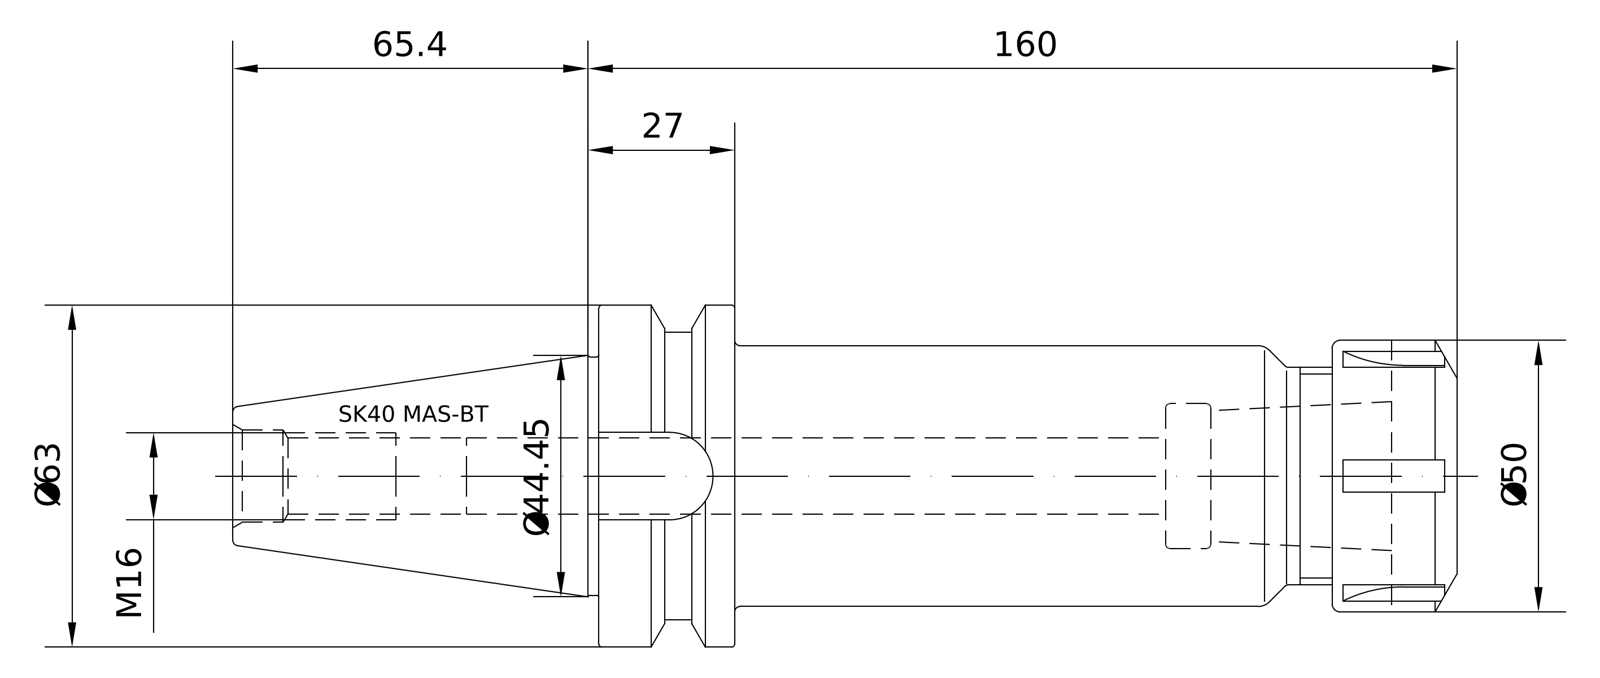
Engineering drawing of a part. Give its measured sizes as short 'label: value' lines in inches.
name: 40-522-32; 83-912-32; 40-522-32_ASM
written by: PRO/ENGINEER BY PARAMETRIC TECHNOLOGY CORPORATION, 2010430 (CONFIG_CONTROL_DESIGN)
unit: in
bodies: 2 solids, 146 faces (52 planar, 32 cylindrical, 62 other)
size: 8.874 × 2.48 × 2.48
volume: 21.06 in³; area: 77.49 in²
holes: 1× ⌀0.545, 1× ⌀0.67, 1× ⌀0.689, 1× ⌀0.925
bosses: 1× ⌀2.48, 1× ⌀2.077, 1× ⌀1.969, 1× ⌀1.89, 1× ⌀1.722, 1× ⌀1.575, 1× ⌀0.63
rounds: 6× R0.106, 1× R0.319
face distances: 0.886, 5.335, 6.22, 0.984, 4.35, 5.236, 5.709, 4.724, 0.374, 0.512
